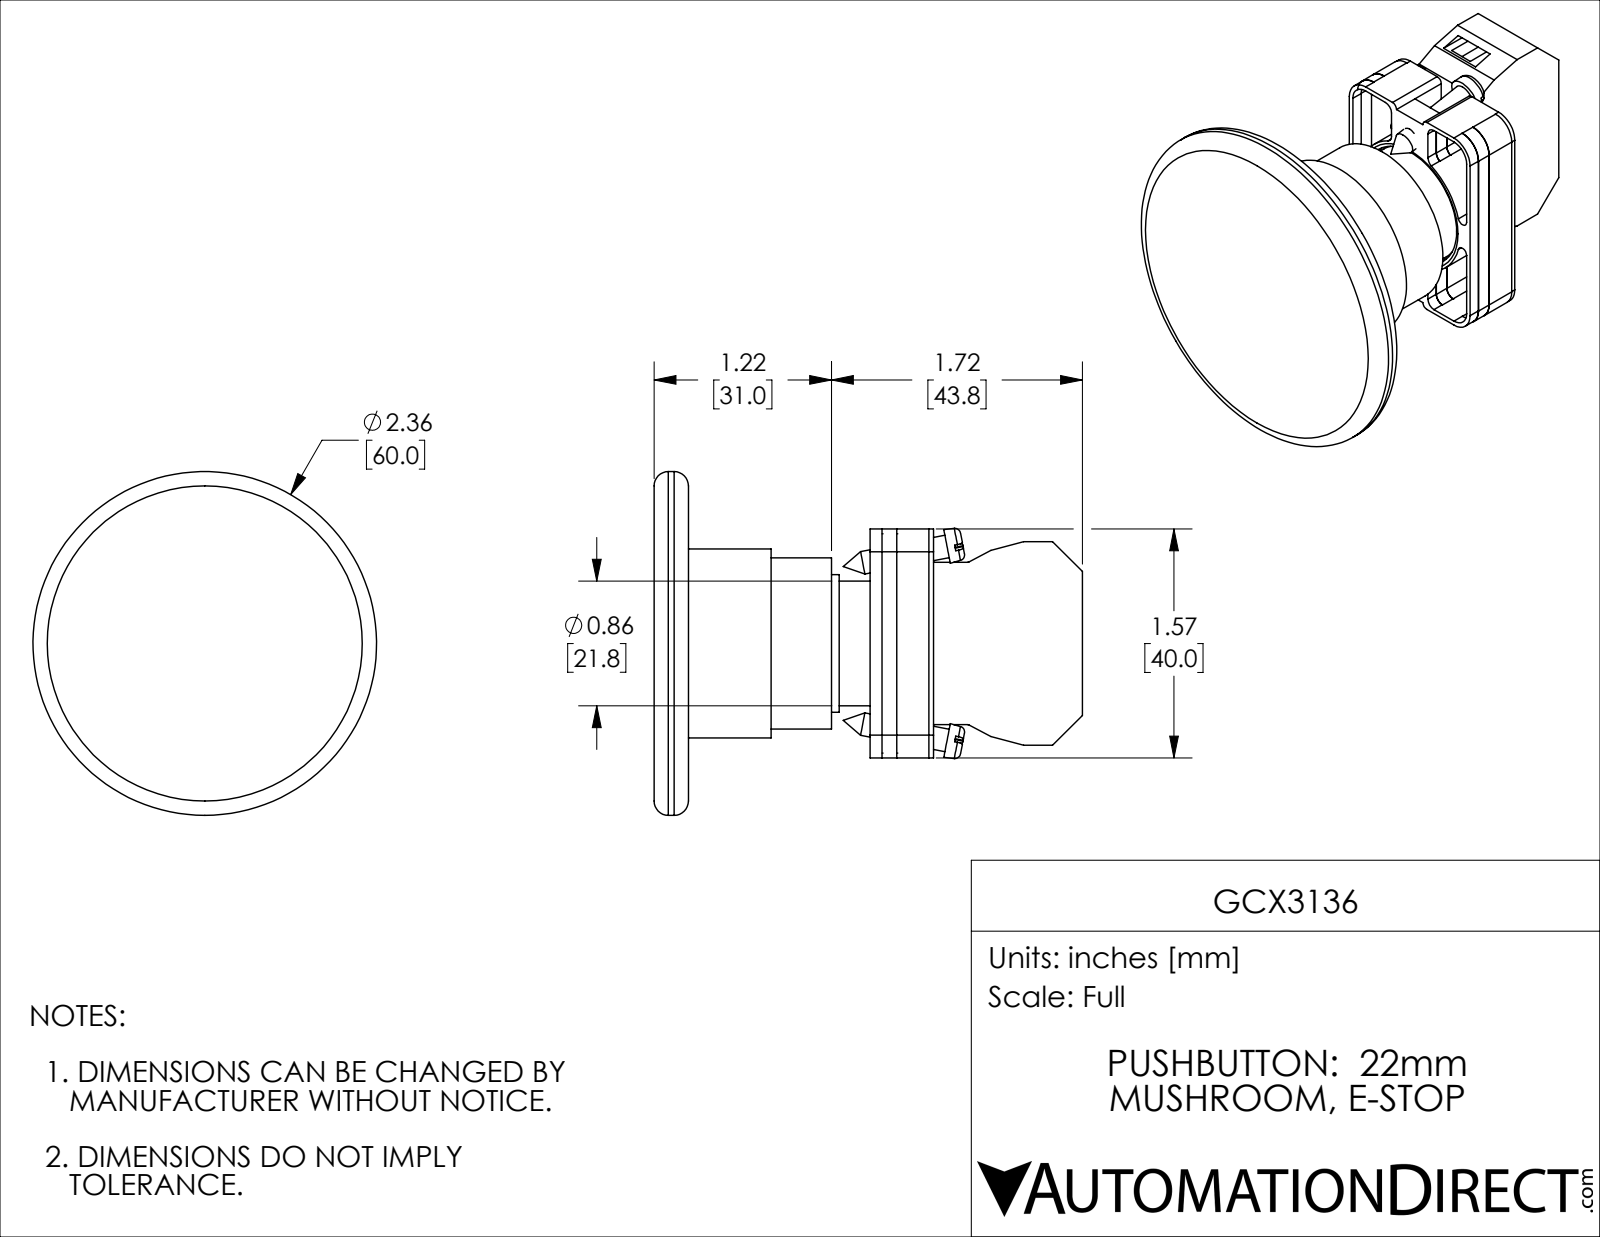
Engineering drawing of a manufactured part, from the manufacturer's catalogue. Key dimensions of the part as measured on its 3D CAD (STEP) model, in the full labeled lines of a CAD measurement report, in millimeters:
Part name (STEP PRODUCT): ecx1030; ECX3029-2; GCX3136 OPERATOR; GCX3136
STEP written by: SolidWorks 2016 (AUTOMOTIVE_DESIGN)
Units: millimetres
Bodies: 6 solids, 391 faces (224 planar, 136 cylindrical, 31 other)
Overall size (bounding box): 74.8 × 60 × 60
Volume: 39 590 mm³ · Surface area: 24 950 mm²
Round holes (diameter × count): ⌀2 ×2, ⌀3.1 ×2, ⌀3.3 ×2, ⌀2.2 ×1, ⌀5 ×1, ⌀22.3 ×1, ⌀22.6 ×1, ⌀26 ×1, ⌀30 ×1
Round bosses / shafts (diameter × count): ⌀4 ×2, ⌀60 ×1, ⌀33 ×1, ⌀29.8 ×1, ⌀24 ×1, ⌀21.7 ×1, ⌀19.8 ×1
Partial cylindrical surfaces — rounded edges, fillets, slot ends (radius × count): R1.5 ×24, R1 ×12, R3.1 ×12, R4 ×12, R1 ×4, R3.3 ×2, R0.5 ×1, R1.6 ×1
Main face-to-face distances: 6, 42.8, 48.8, 14.7, 0.8, 44.8, 2, 4, 0.8, 18.3
Hole centre spacings: 6, 13.8, 12, 12.4
